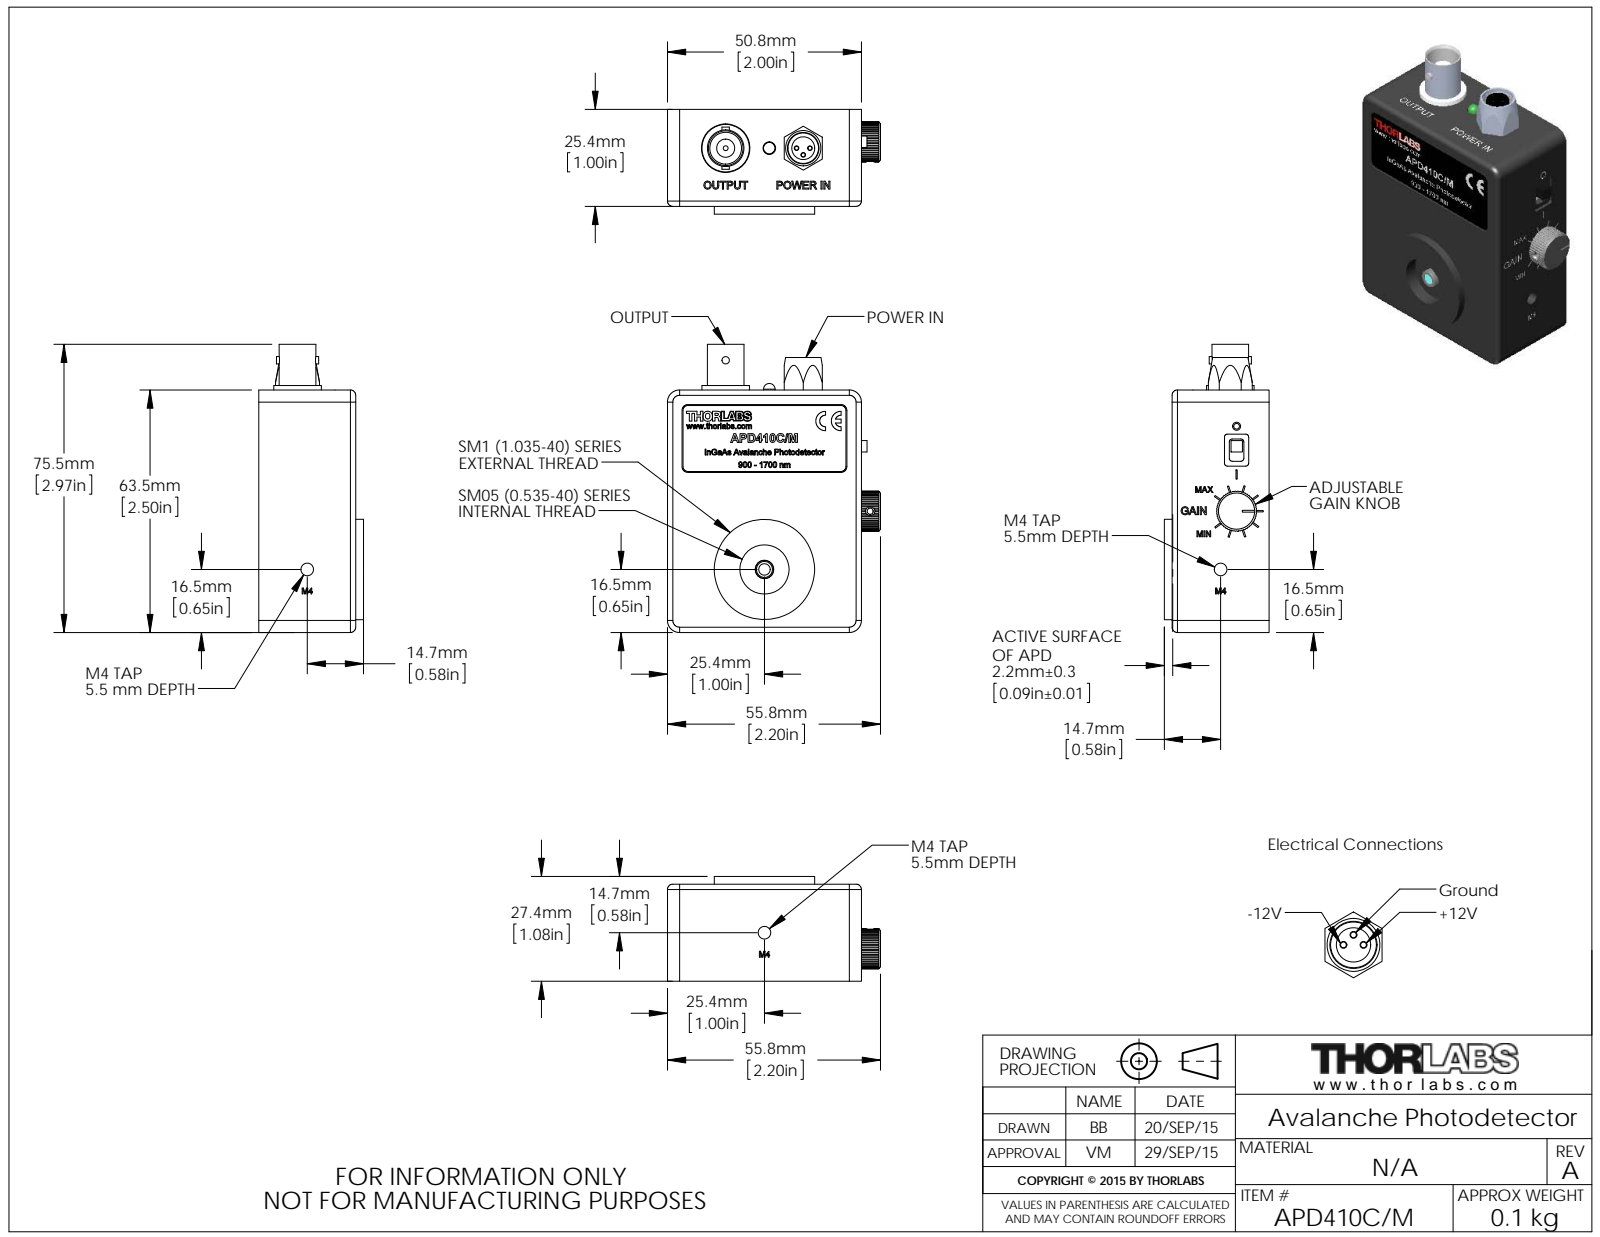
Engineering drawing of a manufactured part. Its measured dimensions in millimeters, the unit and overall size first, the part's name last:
Units: millimetres
Overall size (bounding box): 75.46 × 55.8 × 27.43
Round holes (diameter × count): ⌀1.6 ×9, ⌀0.51 ×6, ⌀2.4 ×4, ⌀0.45 ×2, ⌀2.5 ×2, ⌀3.3 ×2, ⌀1.27 ×1, ⌀1.32 ×1, ⌀2.1 ×1, ⌀3 ×1, ⌀3.3 ×1, ⌀3.5 ×1
Round bosses / shafts (diameter × count): ⌀1 ×5, ⌀3.8 ×4, ⌀2 ×4, ⌀1.64 ×2, ⌀1.6 ×2, ⌀1.3 ×2, ⌀26.29 ×1, ⌀12.45 ×1
Partial cylindrical surfaces — rounded edges, fillets, slot ends (radius × count): R0.3 ×53, R3.17 ×19, R3.3 ×14, R0.79 ×8, R2.41 ×8, R0.5 ×6, R1.91 ×6, R0.2 ×5
Main face-to-face distances: 1.59, 2.54, 0.4, 23.75, 22.16, 25.4, 23.81, 1.65, 25, 23.41
Hole centre spacings: 41.17, 4.41, 51.14, 65.51, 2.49, 43.46, 1.27, 2
Bodies: 0 solids, 2374 faces (1279 planar, 436 cylindrical, 659 other)
Part name (STEP PRODUCT): MTN005412
STEP written by: SolidWorks 2014 (AUTOMOTIVE_DESIGN)
